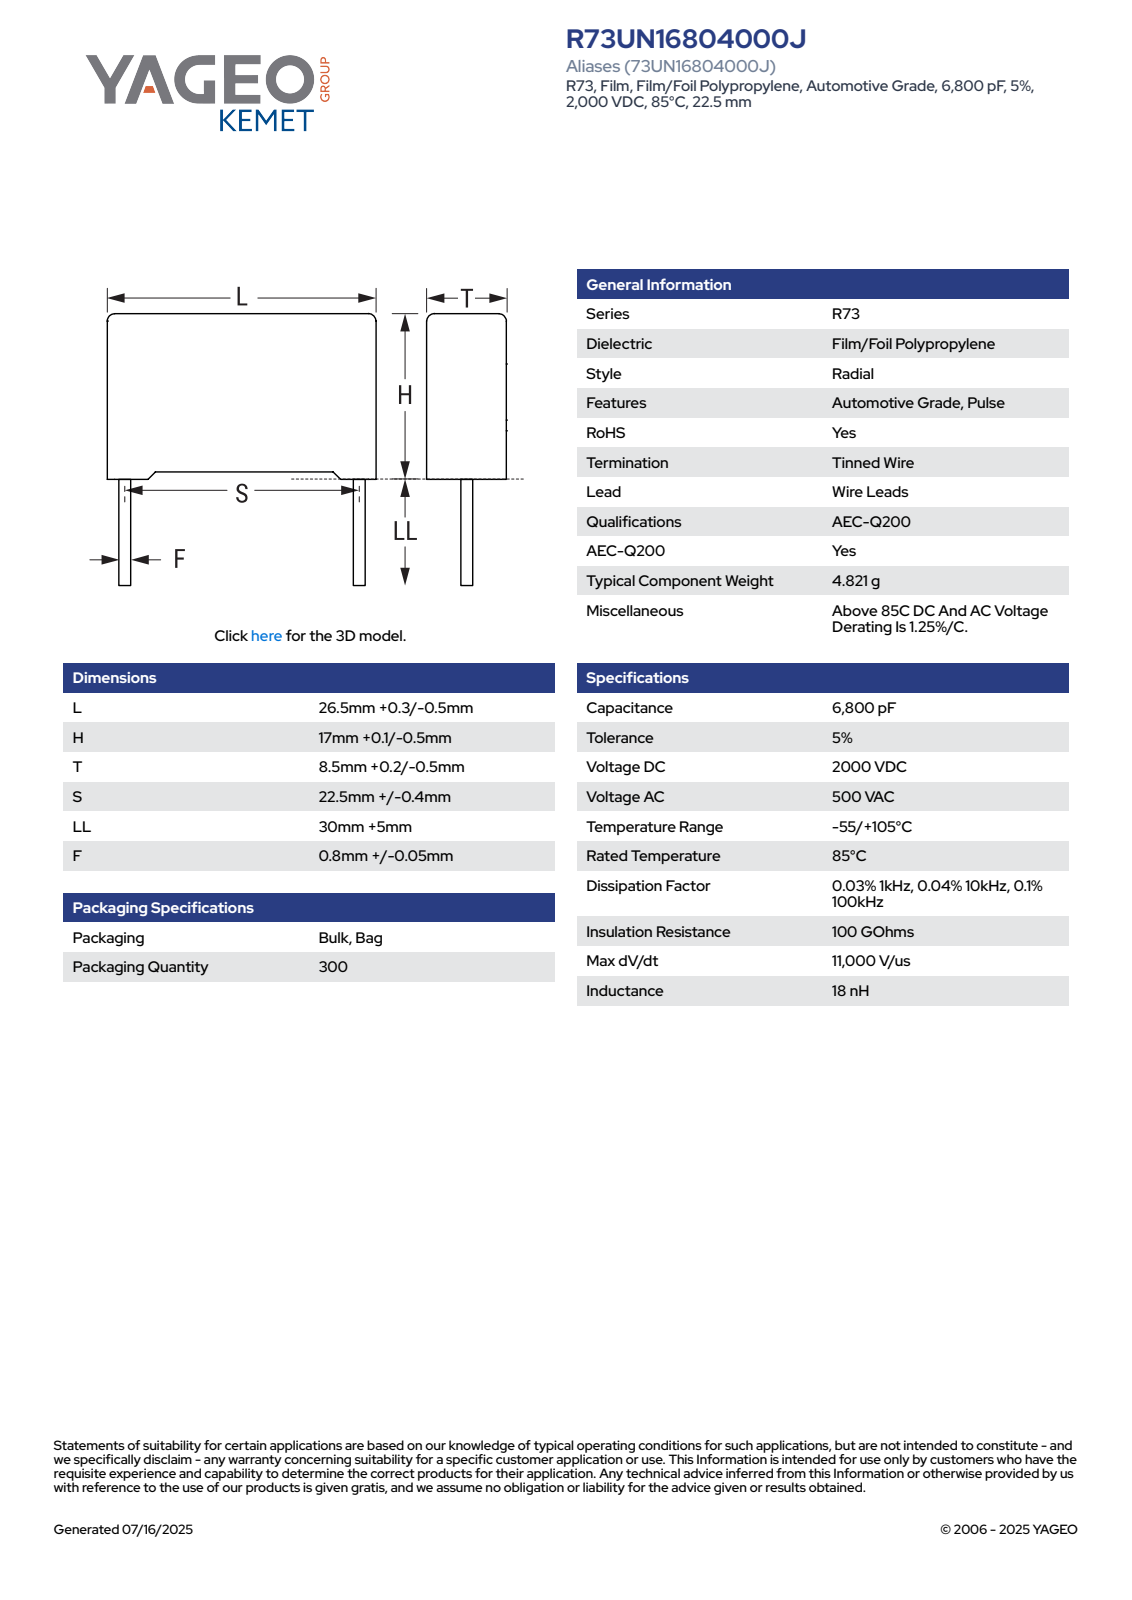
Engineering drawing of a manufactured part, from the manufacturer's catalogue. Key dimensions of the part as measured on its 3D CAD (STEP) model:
Part name (STEP PRODUCT): CFR_RB2_26.5X17X8.5_L26.8H17.1T8.7S22.5LL35F0.85
STEP written by: SolidWorks 2021 (AUTOMOTIVE_DESIGN)
Units: millimetres
Bodies: 4 solids, 85 faces (77 planar, 8 cylindrical, 0 other)
Overall size (bounding box): 52.1 × 26.8 × 8.71
Volume: 3 875 mm³ · Surface area: 1 914 mm²
Round bosses / shafts (diameter × count): ⌀0.85 ×2
Partial cylindrical surfaces — rounded edges, fillets, slot ends (radius × count): R0.5 ×4
Main face-to-face distances: 8.7, 16.35, 26.8, 16.51, 0.89, 0.75, 0.59, 17.1, 7.81, 8.71
